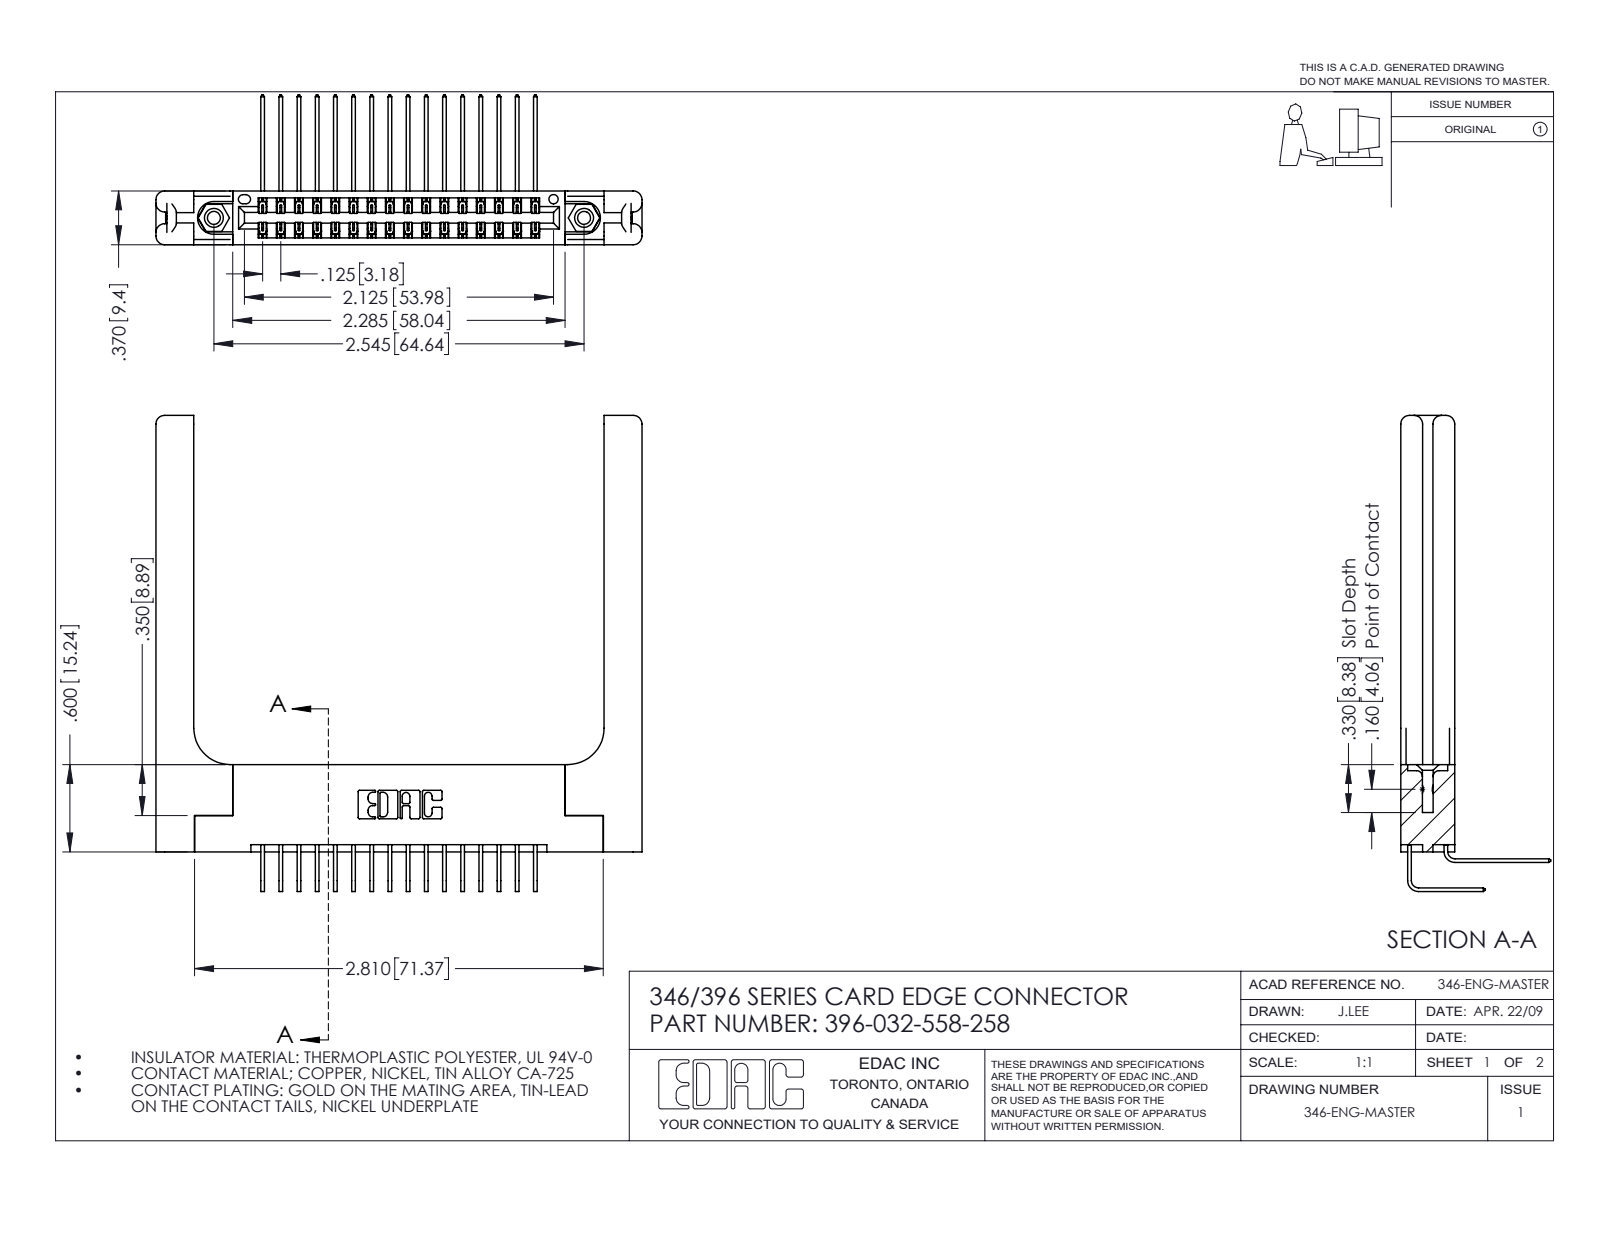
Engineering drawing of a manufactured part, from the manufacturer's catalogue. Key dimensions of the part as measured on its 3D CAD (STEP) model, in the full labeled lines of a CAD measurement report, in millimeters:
Part name (STEP PRODUCT): 346 Part_Flush Mounting Lugs - 0.156 Dia-TH; 346-220-058_345-220-058; 345-292-001_558 559 Tail - 1; 345-250-001_345-250-001-102 (+2 more)
STEP written by: SolidWorks 2016 (CONFIG_CONTROL_DESIGN)
Units: millimetres
Bodies: 37 solids, 2106 faces (1408 planar, 638 cylindrical, 60 other)
Overall size (bounding box): 84.9 × 83.1 × 26.2
Volume: 15 700 mm³ · Surface area: 16 800 mm²
Round holes (diameter × count): ⌀2.3 ×2, ⌀3.2 ×2, ⌀4 ×2, ⌀1.6 ×1
Round bosses / shafts (diameter × count): ⌀3.9 ×2
Partial cylindrical surfaces — rounded edges, fillets, slot ends (radius × count): R0.2 ×48, R0.3 ×22, R1.5 ×16, R0.2 ×6, R0.8 ×6, R0.7 ×3, R0.4 ×2, R0.6 ×2
Main face-to-face distances: 9.4, 8.2, 1.8, 1.2, 3.8, 3.8, 0.6, 7.6, 6.4, 2.6
Hole centre spacings: 6.2, 59.4, 64.6
